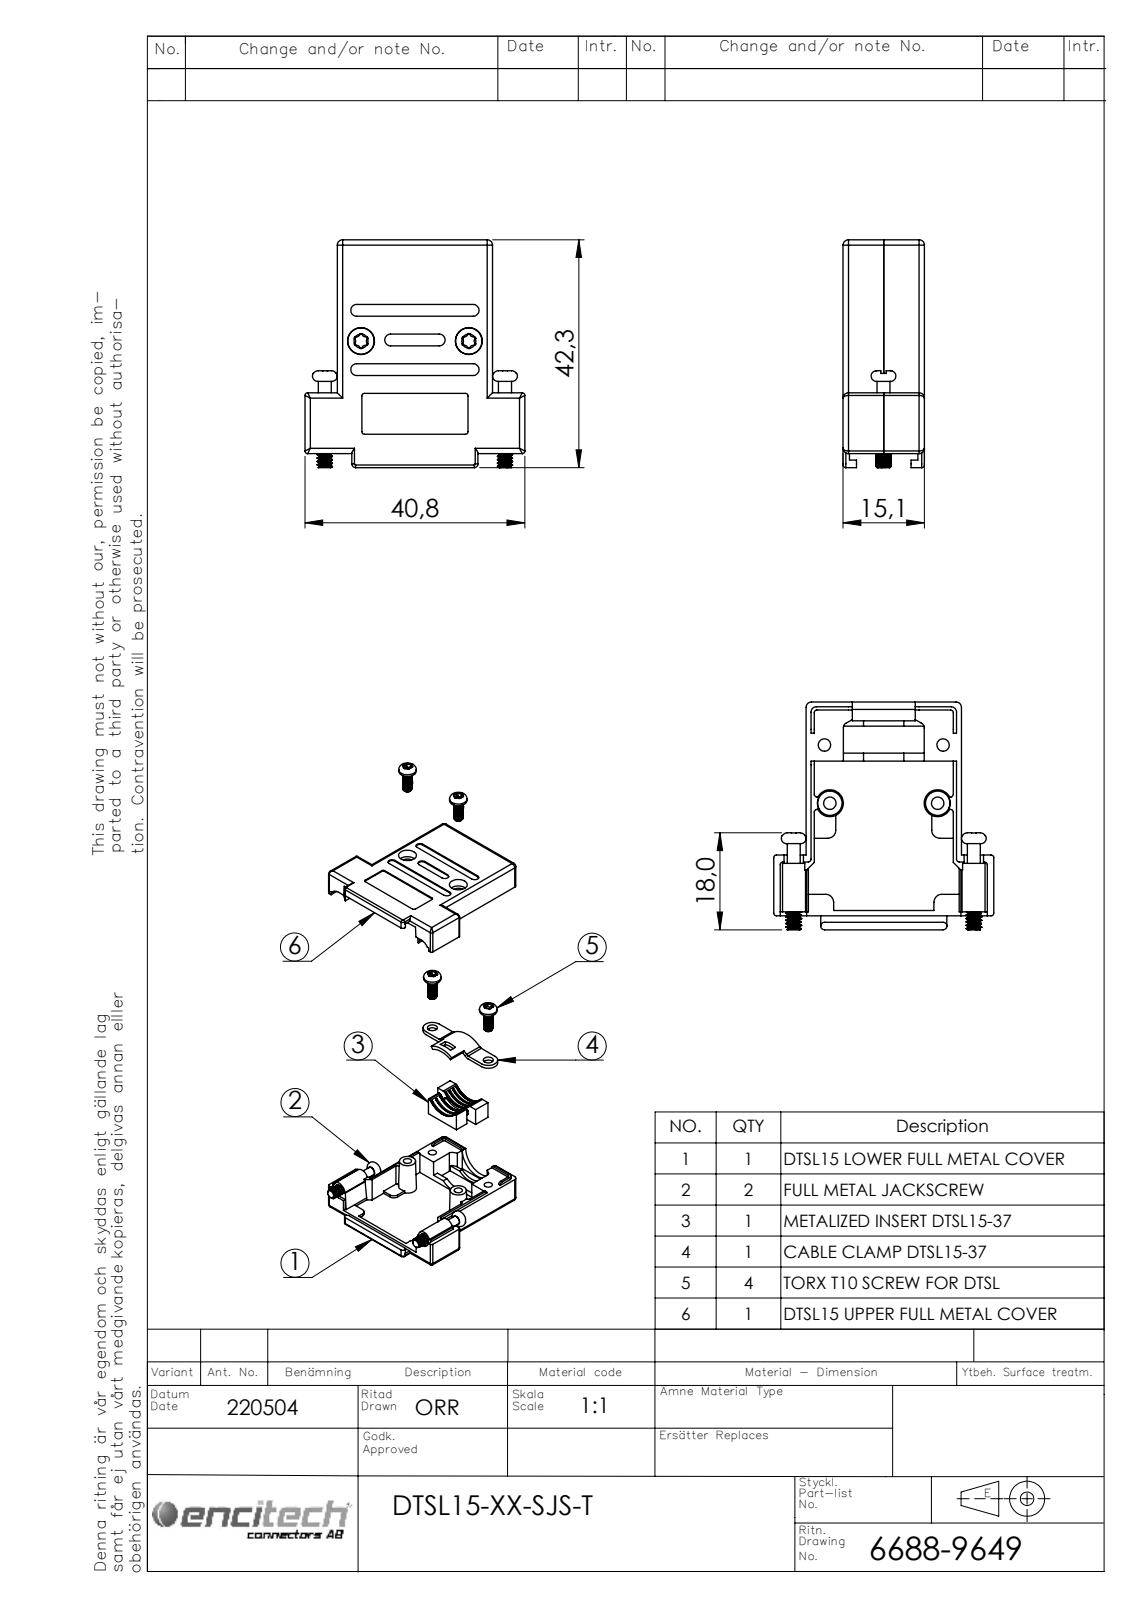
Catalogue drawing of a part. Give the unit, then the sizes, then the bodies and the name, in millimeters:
Units: millimetres
Overall size (bounding box): 42.3 × 40.8 × 15.1
Round holes (diameter × count): ⌀2.3 ×4, ⌀2.8 ×4, ⌀3.1 ×2, ⌀5 ×2, ⌀11.7 ×1
Round bosses / shafts (diameter × count): ⌀4.9 ×4, ⌀2.5 ×4, ⌀2.8 ×2, ⌀2.4 ×2
Partial cylindrical surfaces — rounded edges, fillets, slot ends (radius × count): R0.5 ×30, R0.7 ×30, R0.18 ×24, R1 ×22, R1.1 ×8, R1.5 ×4, R1.8 ×4, R3.62 ×4
Main face-to-face distances: 13.75, 1.35, 15.1, 12.4, 6.2, 7.55, 1.05, 14.8, 7.25, 13.45
Hole centre spacings: 10.85, 16.71, 23.61, 20, 22, 33.42
Volume: 8 278 mm³ · Surface area: 11 895 mm²
Bodies: 14 solids, 959 faces (377 planar, 494 cylindrical, 88 other)
Part name (STEP PRODUCT): 6826-0145-01; 6805-0207-02; 6830-0108-04; 6838-0111-32 (+3 more)
STEP written by: SolidWorks 2021 (AUTOMOTIVE_DESIGN)
